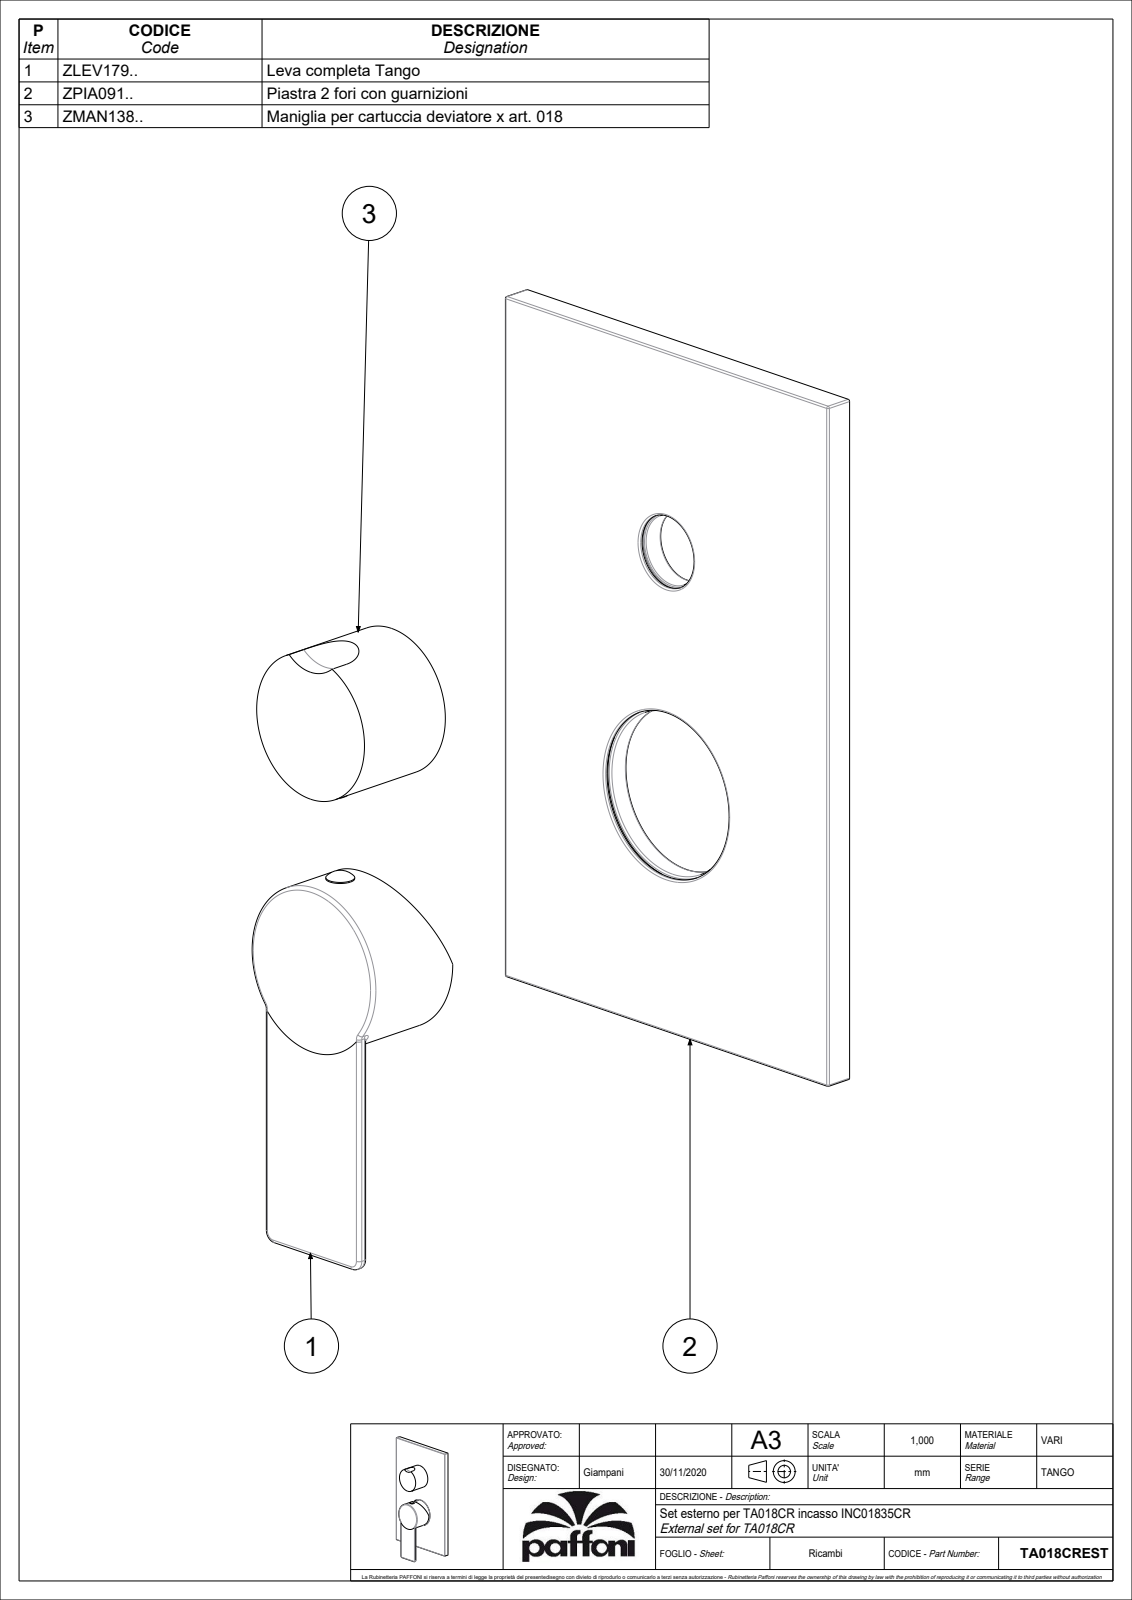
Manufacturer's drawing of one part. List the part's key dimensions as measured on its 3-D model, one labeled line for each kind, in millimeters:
Part name (STEP PRODUCT): TA018CREST
STEP written by: CREO PARAMETRIC BY PTC INC, 2020044 (CONFIG_CONTROL_DESIGN)
Units: millimetres
Bodies: 3 solids, 279 faces (99 planar, 96 cylindrical, 84 other)
Overall size (bounding box): 204 × 120 × 40.35
Volume: 158 078 mm³ · Surface area: 101 555 mm²
Round holes (diameter × count): ⌀3 ×2, ⌀3.2 ×1, ⌀4.2 ×1, ⌀14.8 ×1, ⌀19.2 ×1, ⌀20 ×1, ⌀21 ×1, ⌀23.2 ×1, ⌀36 ×1, ⌀45 ×1, ⌀46 ×1, ⌀47 ×1
Round bosses / shafts (diameter × count): ⌀7.6 ×2, ⌀5.5 ×2, ⌀51 ×1, ⌀49 ×1, ⌀45.5 ×1, ⌀40 ×1, ⌀25 ×1, ⌀24 ×1
Partial cylindrical surfaces — rounded edges, fillets, slot ends (radius × count): R1 ×14, R0.5 ×10, R1.5 ×4, R3 ×2, R3.5 ×1, R12.5 ×1
Main face-to-face distances: 2.5, 0.5, 3, 8, 5.5, 5, 31.5, 31, 22.5, 34.5
Hole centre spacings: 1, 10, 68, 78
